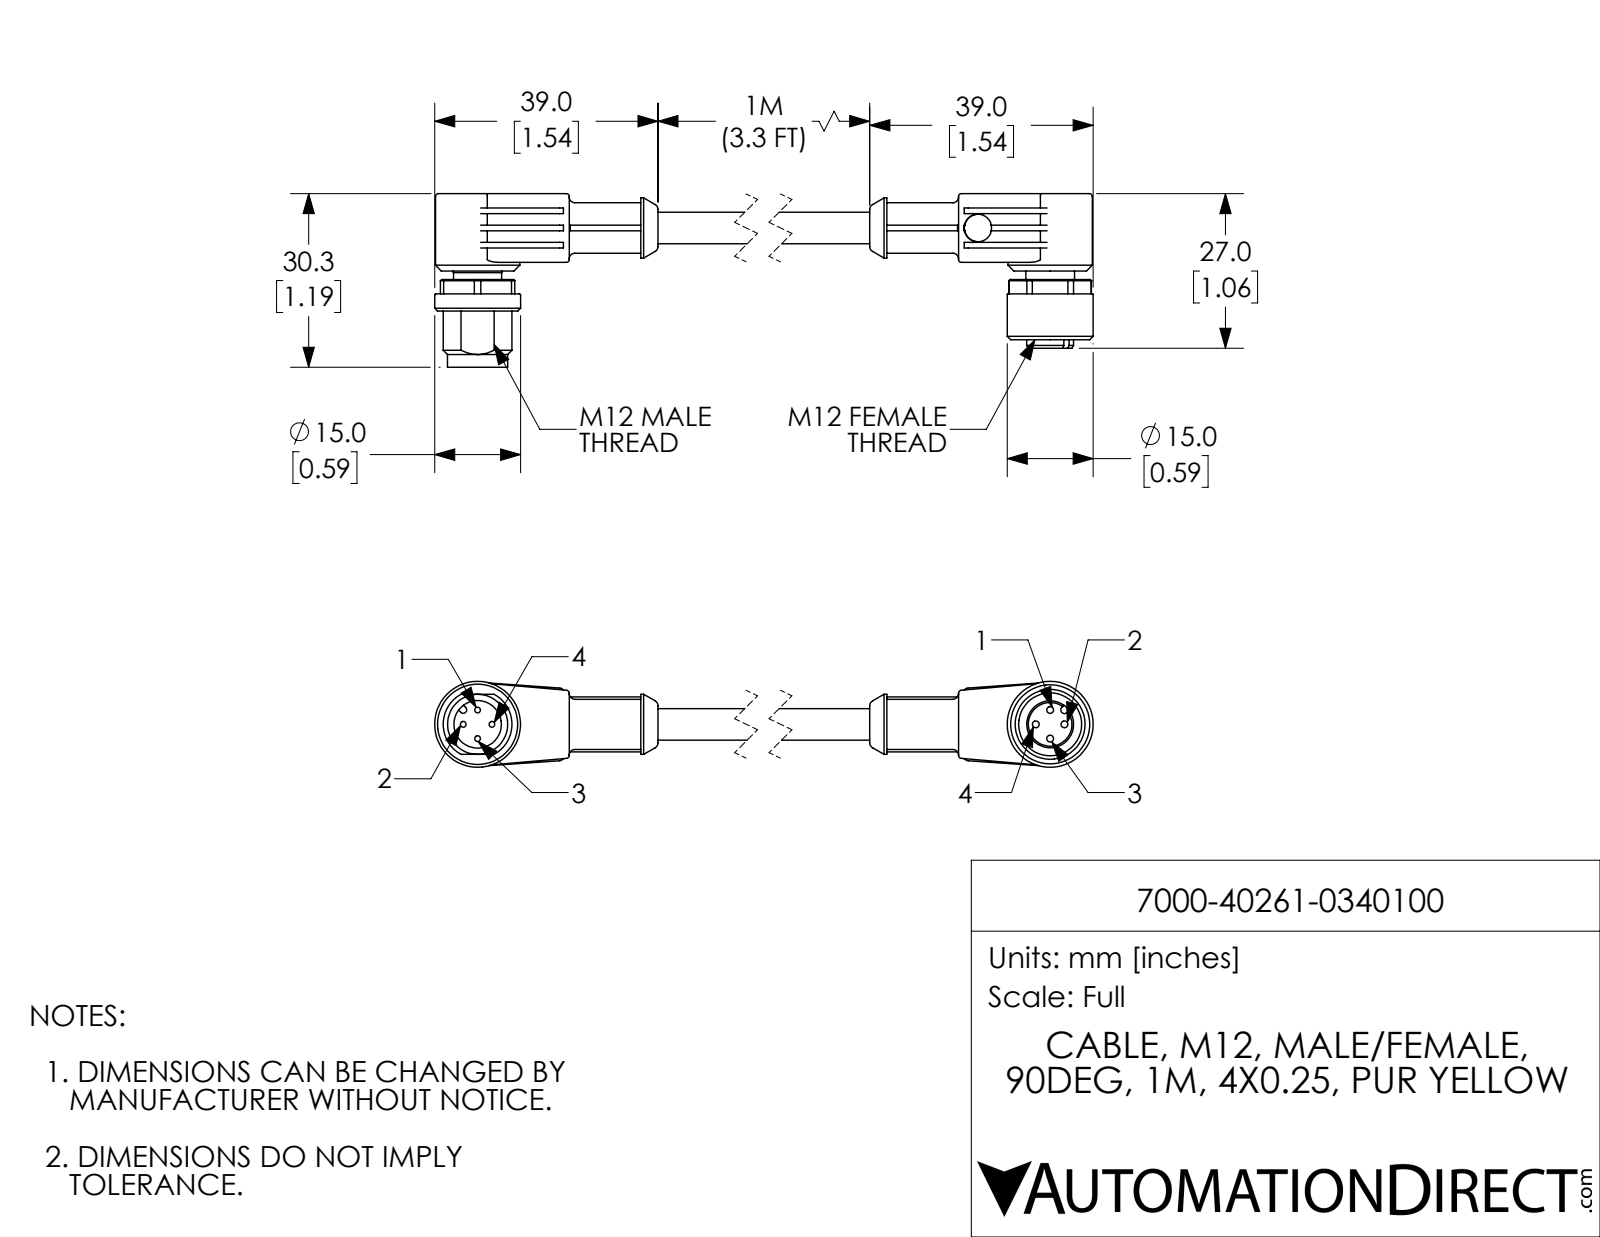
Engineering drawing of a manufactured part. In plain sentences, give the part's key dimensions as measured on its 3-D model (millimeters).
The part is named "7000-40261-0340100; 7000-40261-0340100_MALE; 7000-40261-0340100_FEMALE". Its 3-D file was written by "SolidWorks 2021 (CONFIG_CONTROL_DESIGN)". It is 2 solids with 290 faces: 123 planar, 104 cylindrical and 63 other. Overall it measures 130 by 30.3 by 15 millimeters. Its volume is 13 600 cubic millimeters and its surface area 7 019 square millimeters. Round holes: 4 of diameter 1.2, 2 of diameter 4.8, 1 of diameter 8.3, 1 of diameter 11. Round bosses or shafts: 4 of diameter 1, 2 of diameter 15, 2 of diameter 14.7, 2 of diameter 10.5, 1 of diameter 8.8, 1 of diameter 8.5, 1 of diameter 8.5, 1 of diameter 8.4. Partial cylindrical surfaces (rounded edges, fillets, slot ends): 16 of radius 0.5, 4 of radius 1, 2 of radius 7.2, 1 of radius 0.6, 1 of radius 0.7, 1 of radius 6. The main face-to-face distances are 12, 1.5, 3, 15, 13.5, 4.5, 5.5, 2.5, 9.5, 6.5. The hole center spacings are 2.5, 3.5, 5, 115, 90.5, 112.5, 115, 117.5.
